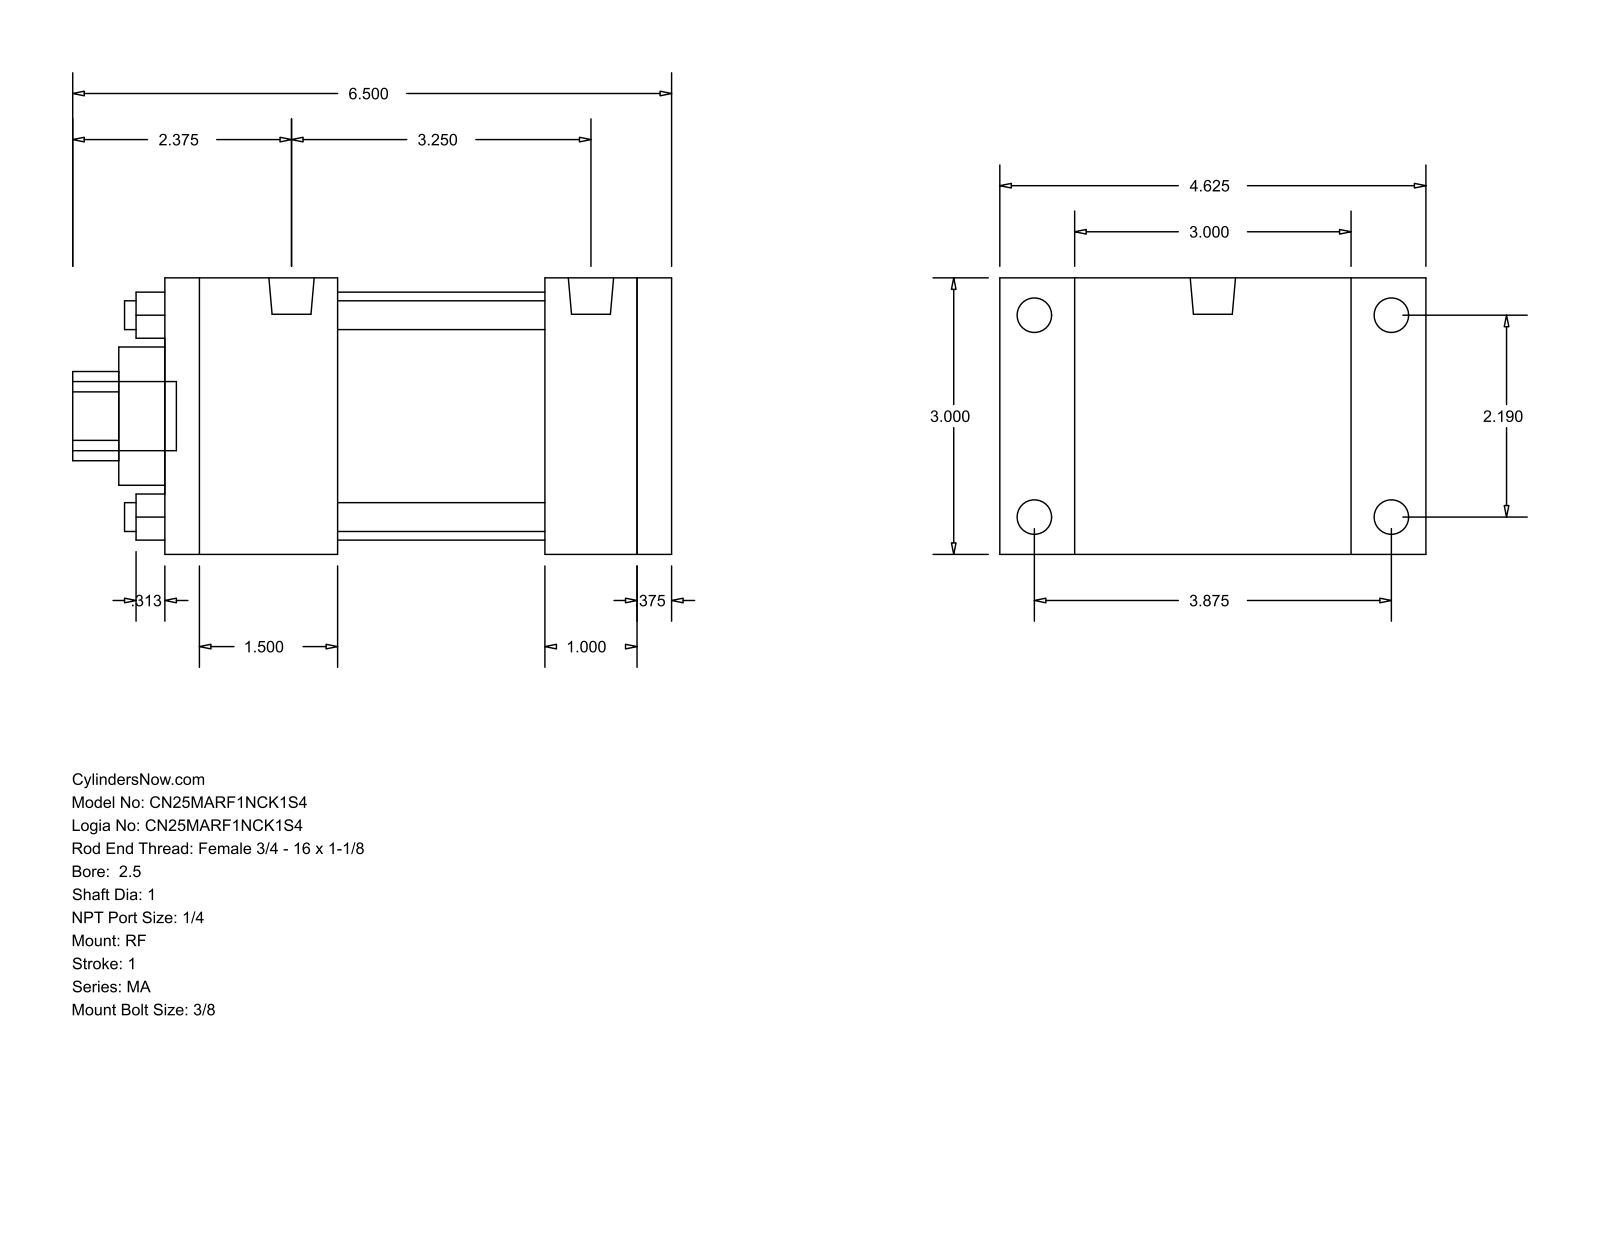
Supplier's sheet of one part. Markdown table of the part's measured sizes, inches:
| quantity | value |
| --- | --- |
| part name | MA_RF__0250_1 |
| STEP written by | GSSL Pune (CONFIG_CONTROL_DESIGN) |
| units | inches |
| bodies | 0 solids, 92 faces (64 planar, 28 cylindrical, 0 other) |
| overall size | 6.5 × 4.625 × 3 |
| round holes (diameter × count) | 0.313 × 4, 1 × 1, 1.5 × 1, 2.69 × 1 |
| round bosses / shafts (diameter × count) | 0.375 × 4, 0.313 × 4, 0.492 × 2, 0.75 × 1 |
| partial cylindrical surfaces (radius × count) | 0.484 × 1 |
| main face-to-face distances | 3, 5.5, 0.375, 5.125, 1.875, 4.125, 2.25, 3.25, 3.625, 1 |
| hole center spacings | 1.548, 2.19, 3.097 |
